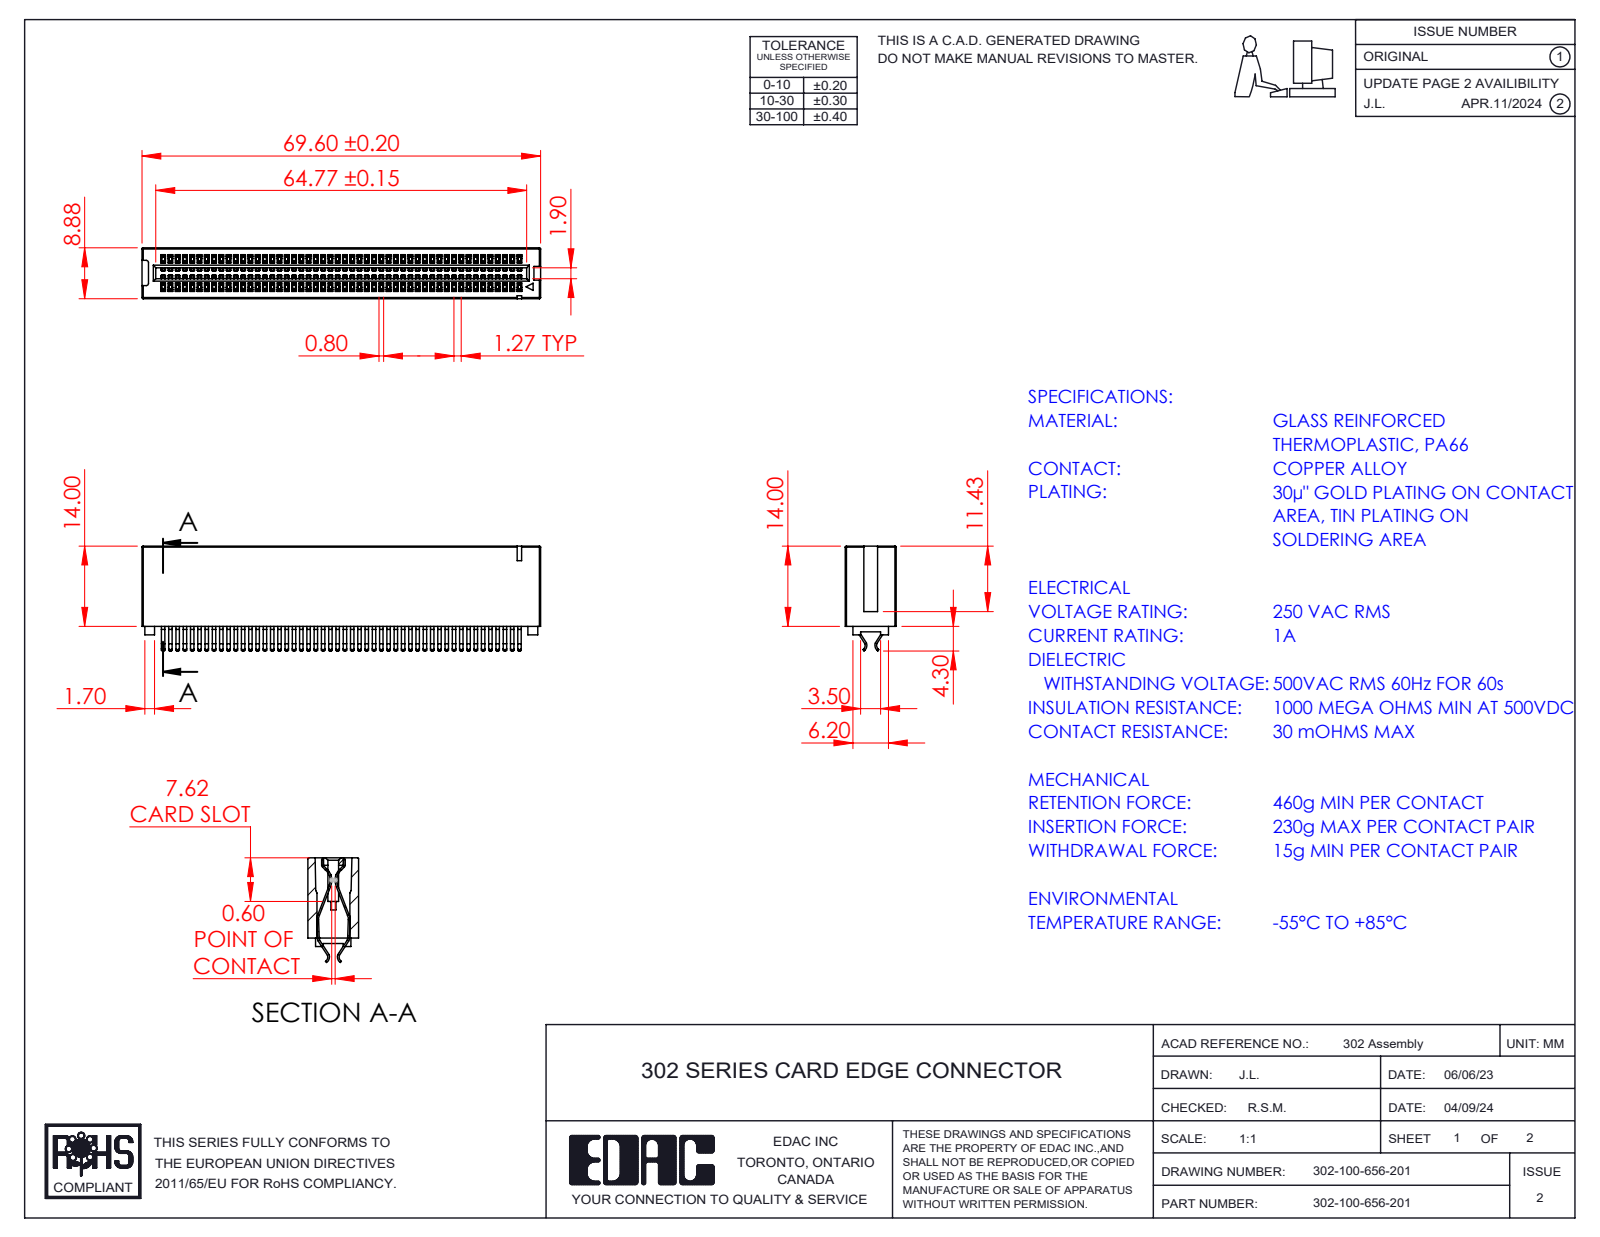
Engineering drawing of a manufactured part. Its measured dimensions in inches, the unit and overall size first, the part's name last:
Units: inches
Overall size (bounding box): 2.74 × 0.72 × 0.35
Partial cylindrical surfaces — rounded edges, fillets, slot ends (radius × count): R0.008 ×308, R0.004 ×2, R0.016 ×2, R0.016 ×2, R0.037 ×2, R0.041 ×2, R0.048 ×2, R0.049 ×2
Main face-to-face distances: 0.35, 0.05, 0.031, 0.1, 0.15, 0.019, 0.075, 0.137, 0.212, 0.15
Volume: 0.326 in³ · Surface area: 23.6 in²
Bodies: 101 solids, 4816 faces (3199 planar, 1613 cylindrical, 4 other)
Part name (STEP PRODUCT): HSG_Vertical HSG; Contact_302-290-X56; 302-100-656-201
STEP written by: SolidWorks 2023 (CONFIG_CONTROL_DESIGN)
